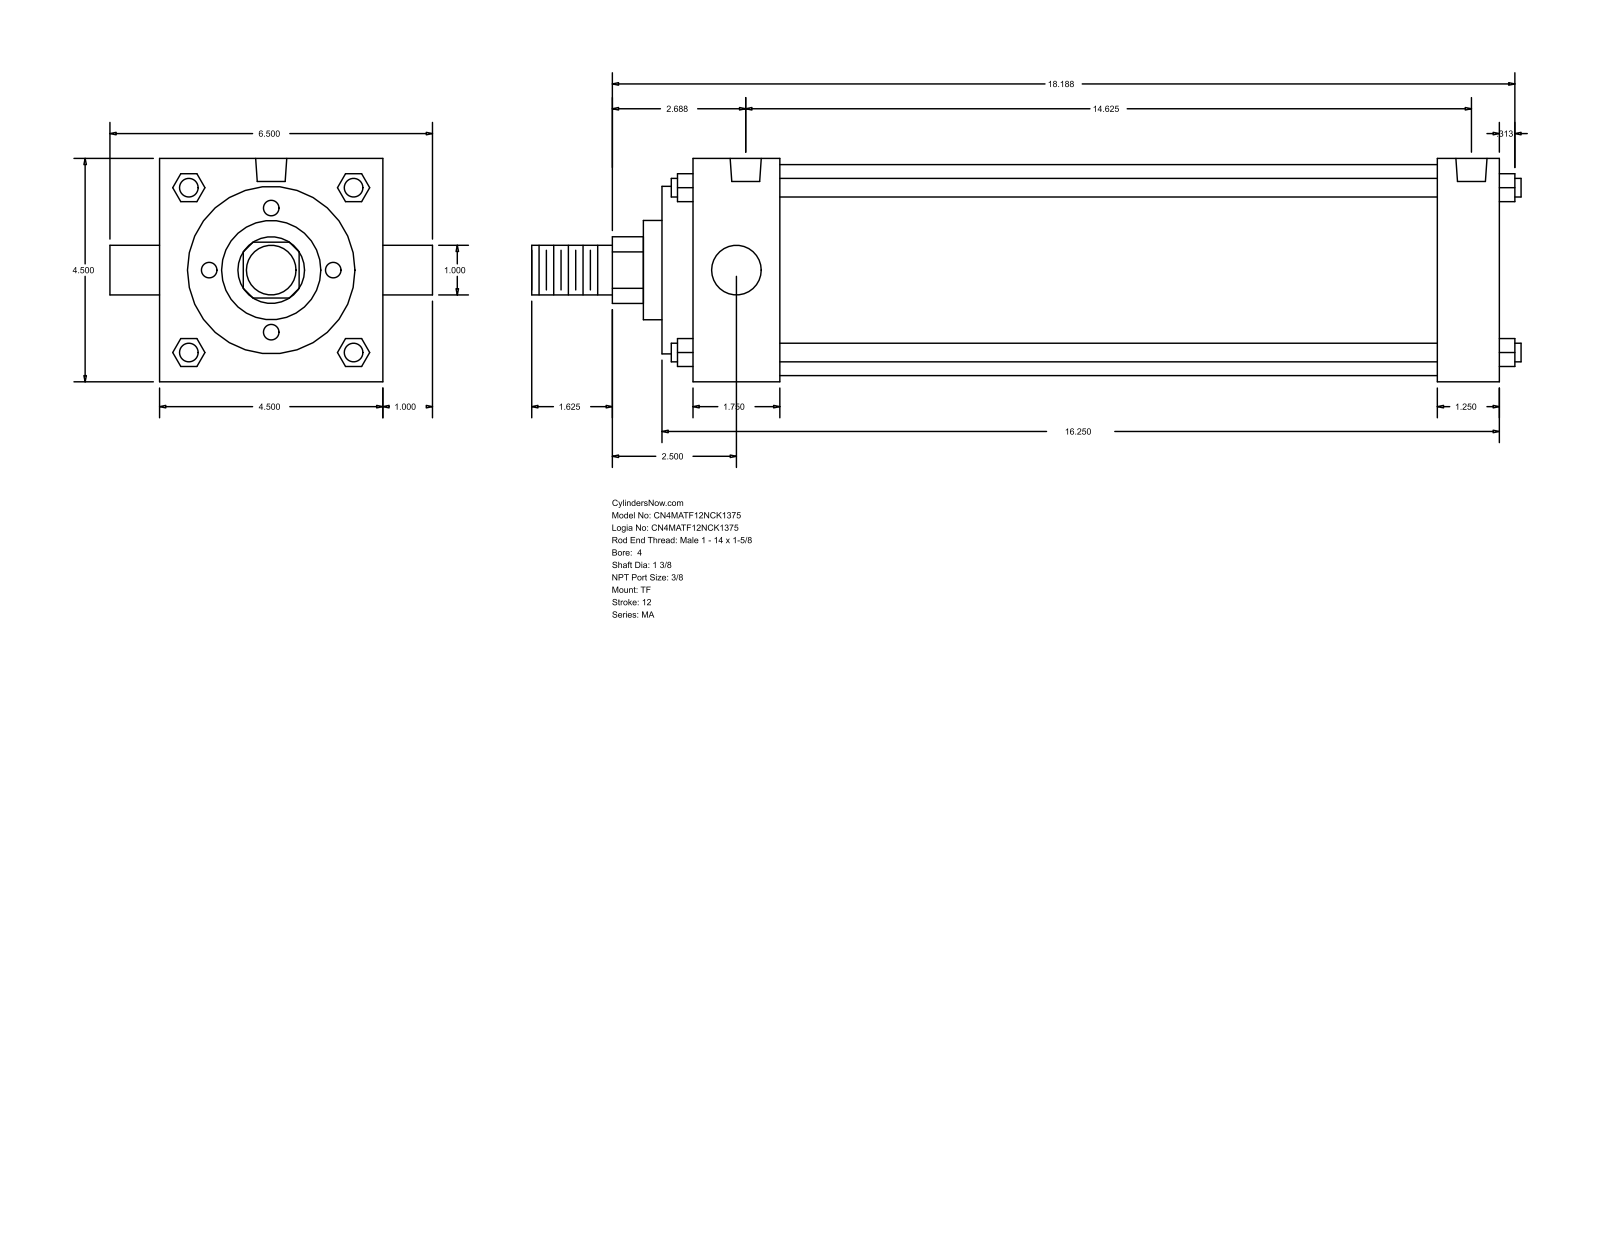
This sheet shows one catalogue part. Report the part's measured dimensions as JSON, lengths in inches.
{"part_name": "MA_TF__0400_1.375", "step_written_by": "GSSL Pune (CONFIG_CONTROL_DESIGN)", "units": "inches", "bodies": {"solids": 0, "faces": 122, "planar": 93, "cylindrical": 29, "other": 0}, "overall_size": [19.937, 6.5, 4.5], "round_holes": [[0.437, 3], [0.627, 2]], "round_bosses_or_shafts": [[0.375, 4], [1, 2], [4.25, 1], [3.375, 1], [2, 1], [1.375, 1]], "partial_cylinders_radius": [[0.672, 1]], "face_to_face_distances": [4.5, 16.25, 16.875, 0.625, 15.625, 15, 1.25, 2.375, 1.75, 13.25], "hole_center_spacings": [0.187, 0.188, 14.25, 14.437, 14.438, 14.625]}
